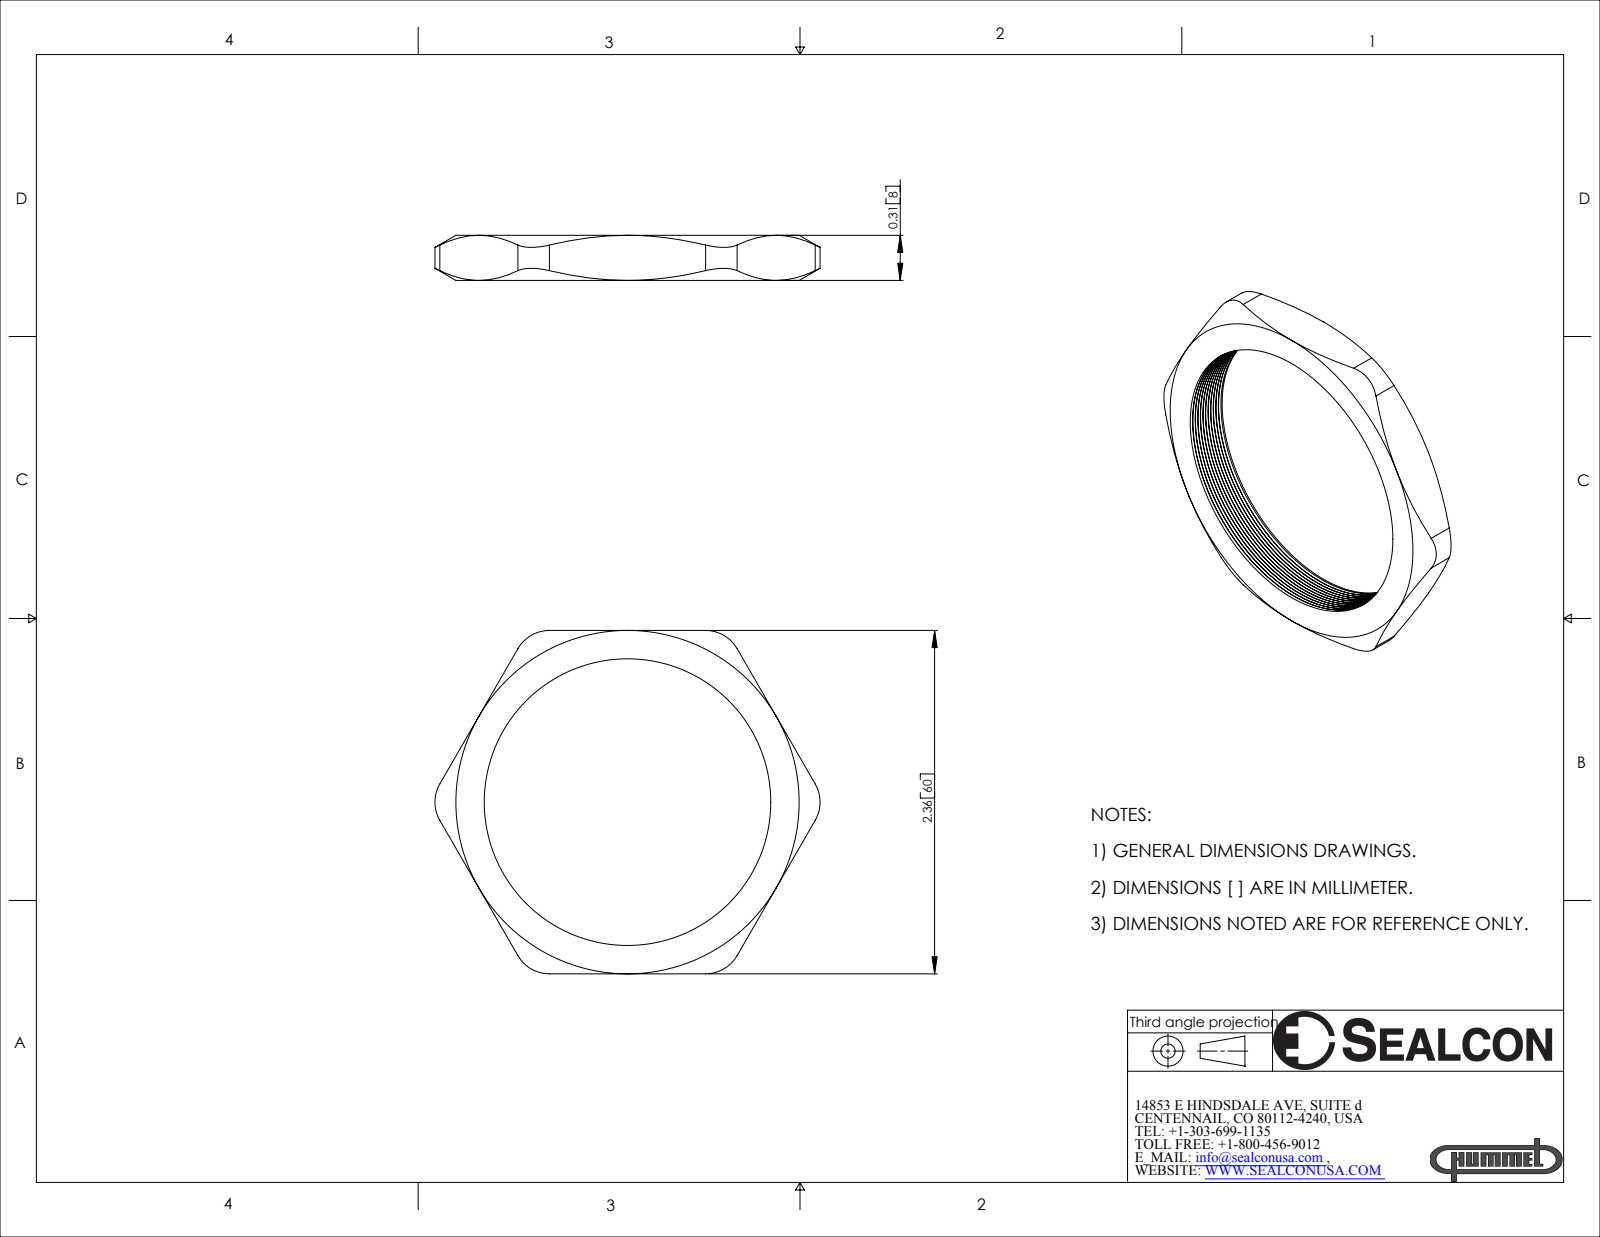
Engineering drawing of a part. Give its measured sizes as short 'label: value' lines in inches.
name: NM-50
written by: SolidWorks 2007 (CONFIG_CONTROL_DESIGN)
unit: in
bodies: 1 solid, 101 faces (8 planar, 31 cylindrical, 62 other)
size: 2.648 × 2.36 × 0.31
volume: 0.502 in³; area: 9.258 in²
holes: 1× ⌀1.97
rounds: 6× R0.25
face distances: 0.31, 2.36
